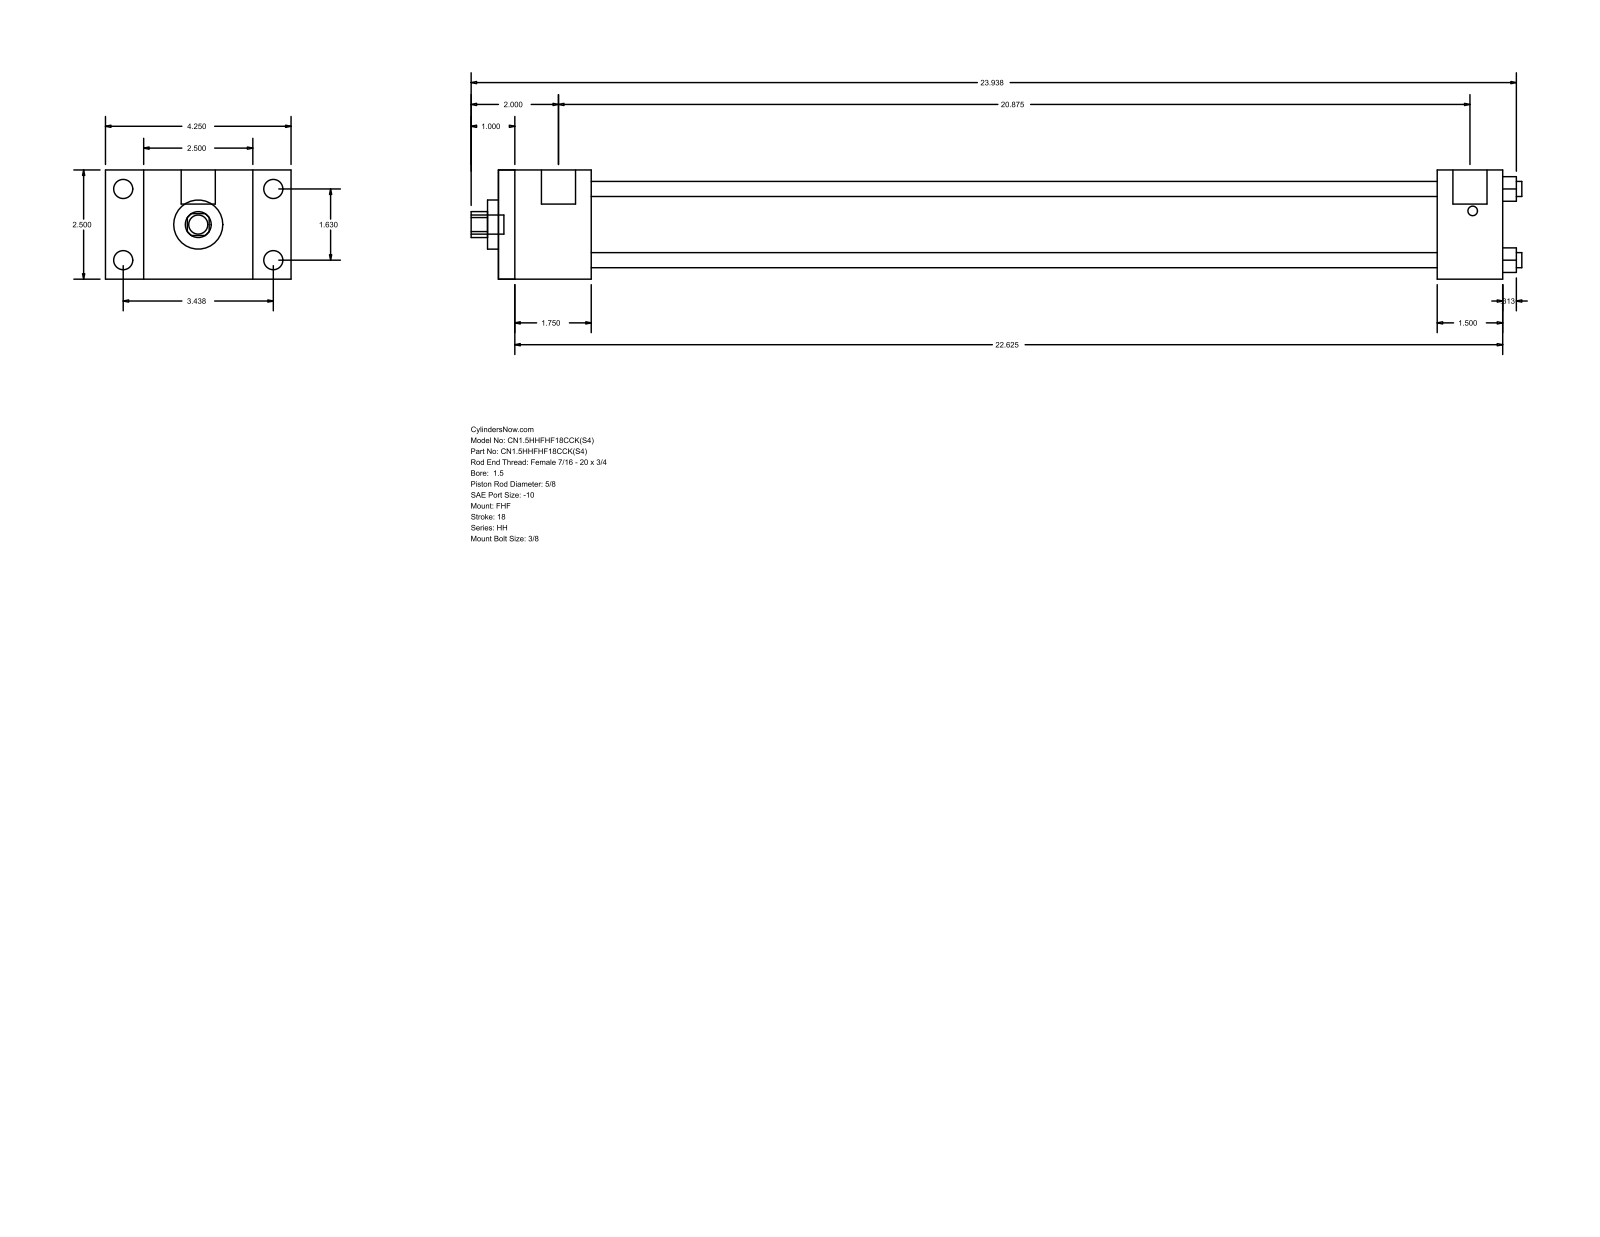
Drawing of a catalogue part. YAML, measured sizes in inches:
part_name: "HH_FHF__0150_0.625"
step_written_by: "GSSL Pune (CONFIG_CONTROL_DESIGN)"
units: inches
bodies: {solids: 0, faces: 88, planar: 60, cylindrical: 28, other: 0}
overall_size: [24.063, 4.25, 2.5]
round_holes:
  - {diameter: 0.345, count: 4}
  - {diameter: 0.625, count: 1}
  - {diameter: 1.125, count: 1}
  - {diameter: 1.75, count: 1}
round_bosses_or_shafts:
  - {diameter: 0.438, count: 4}
  - {diameter: 0.219, count: 4}
  - {diameter: 0.781, count: 2}
  - {diameter: 0.437, count: 1}
partial_cylinders:
  - {radius: 0.297, count: 1}
face_to_face_distances: [2.5, 0.875, 3.375, 2.125, 4.25, 23, 20.875, 1.5, 21.5, 19.375]
hole_center_spacings: [1.152, 1.63, 2.305]
